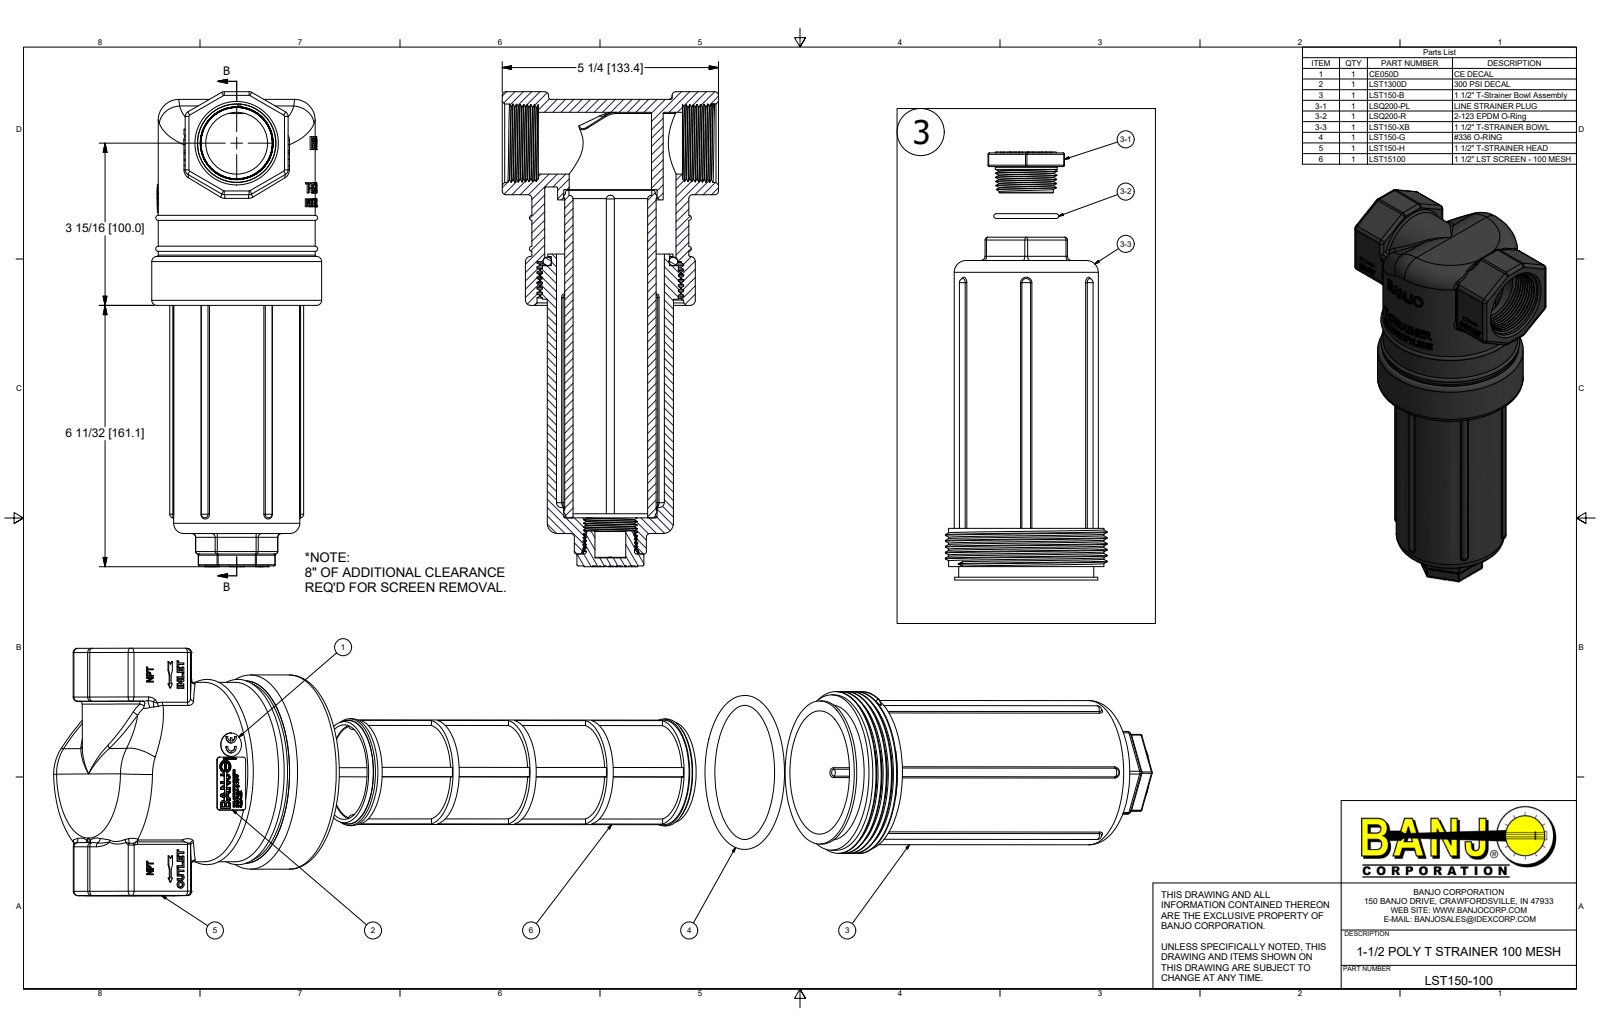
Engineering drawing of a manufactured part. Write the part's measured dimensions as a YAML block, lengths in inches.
part_name: "LST150-100; CE050D; LST1300D; LST150-B (+6 more)"
step_written_by: "Autodesk Inventor 2018 (AUTOMOTIVE_DESIGN)"
units: inches
bodies: {solids: 8, faces: 3130, planar: 1701, cylindrical: 290, other: 1139}
overall_size: [11.53, 5.25, 4.125]
volume: 49.55
surface_area: 482.1
round_holes:
  - {diameter: 0.181, count: 1}
  - {diameter: 0.257, count: 1}
  - {diameter: 0.75, count: 1}
  - {diameter: 1.5, count: 1}
  - {diameter: 1.81, count: 1}
  - {diameter: 1.97, count: 1}
  - {diameter: 2, count: 1}
  - {diameter: 2.26, count: 1}
  - {diameter: 2.265, count: 1}
  - {diameter: 2.62, count: 1}
  - {diameter: 3.19, count: 1}
  - {diameter: 3.425, count: 1}
round_bosses_or_shafts:
  - {diameter: 4.125, count: 1}
  - {diameter: 3.81, count: 1}
  - {diameter: 3.435, count: 1}
  - {diameter: 3.3, count: 1}
  - {diameter: 3.063, count: 1}
  - {diameter: 3.04, count: 1}
  - {diameter: 2.87, count: 1}
  - {diameter: 2.563, count: 1}
partial_cylinders:
  - {radius: 0.03, count: 44}
  - {radius: 0.09, count: 34}
  - {radius: 0.06, count: 16}
  - {radius: 0.125, count: 10}
  - {radius: 0.078, count: 6}
  - {radius: 0.094, count: 6}
  - {radius: 0.1, count: 4}
  - {radius: 0.026, count: 2}
face_to_face_distances: [2.5, 10.157, 0.92, 1.24, 1.75, 0.875, 9.845, 0.313, 3.5, 0.187]
